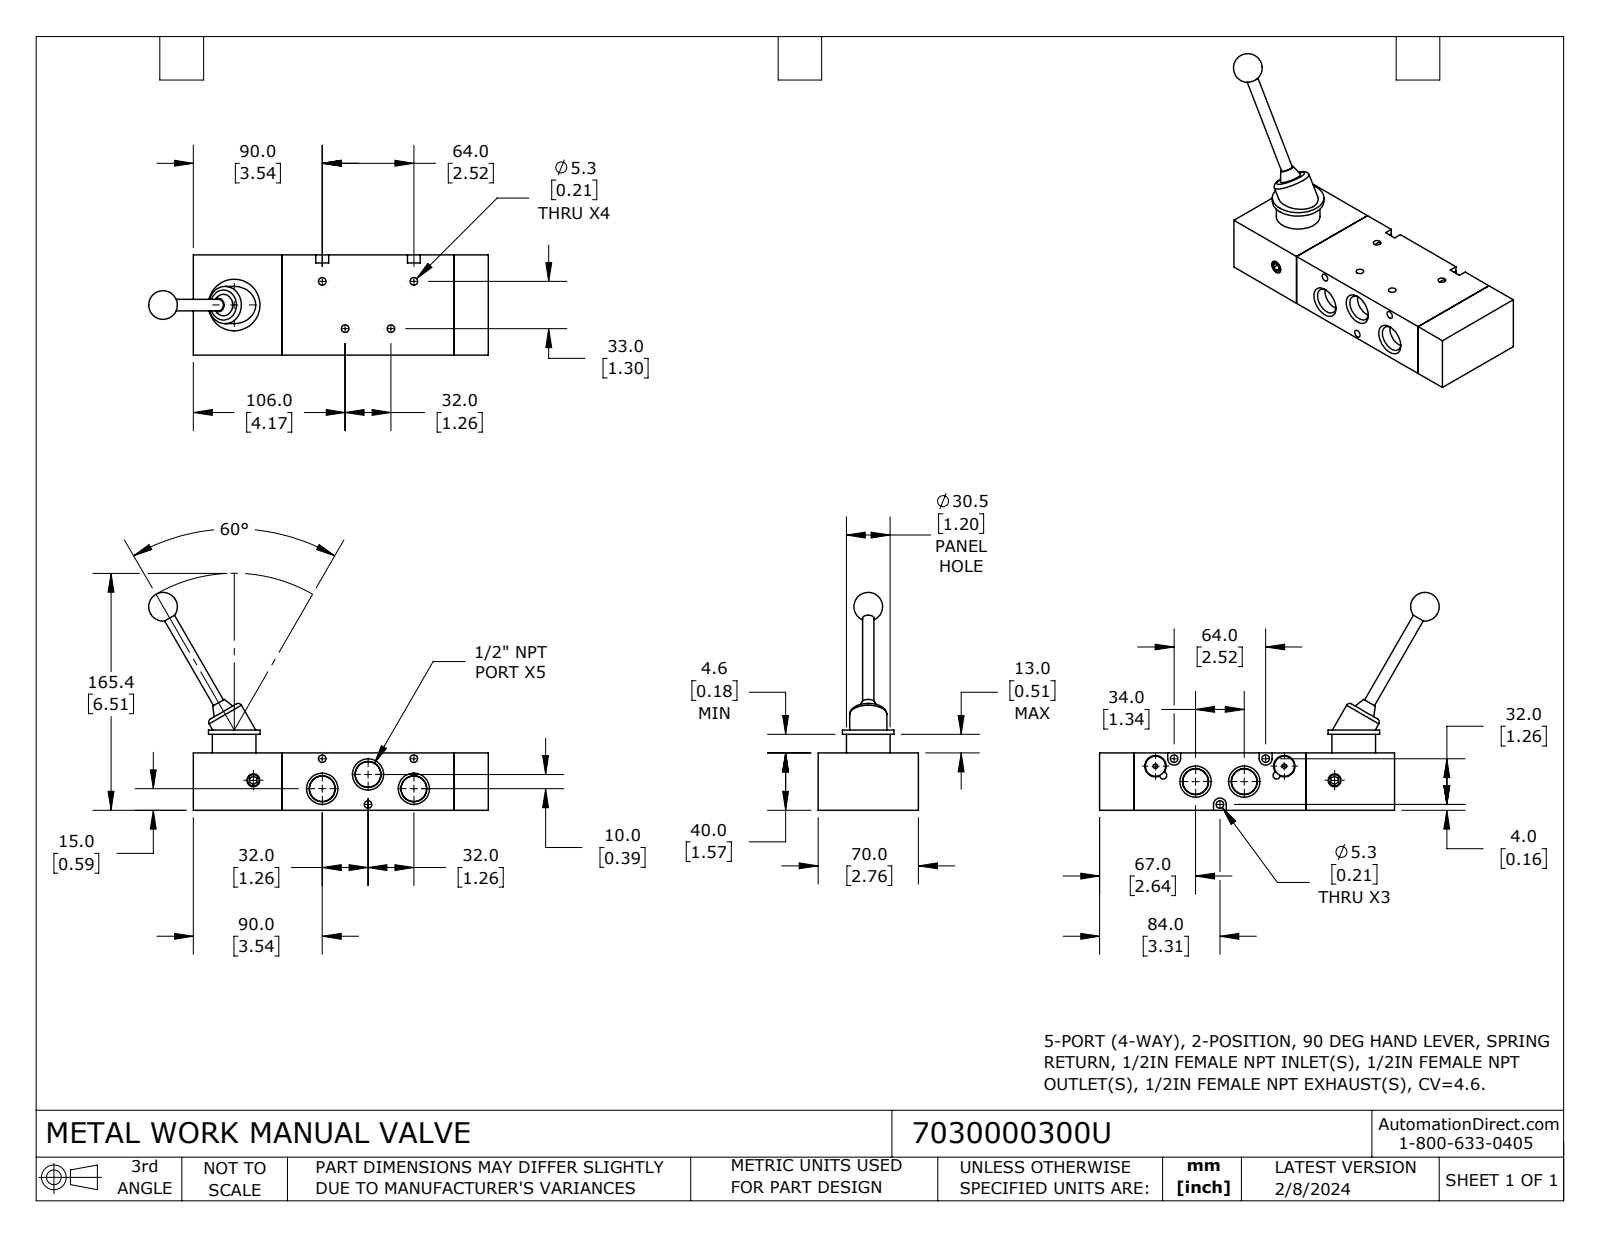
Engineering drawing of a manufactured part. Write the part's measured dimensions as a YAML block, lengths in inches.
part_name: "7030000300U"
step_written_by: "SolidWorks 2023 (CONFIG_CONTROL_DESIGN)"
units: inches
bodies: {solids: 3, faces: 155, planar: 72, cylindrical: 57, other: 26}
overall_size: [9.339, 5.988, 2.756]
volume: 35.65
surface_area: 120.8
round_holes:
  - {diameter: 0.209, count: 7}
  - {diameter: 0.587, count: 2}
  - {diameter: 0.354, count: 1}
round_bosses_or_shafts:
  - {diameter: 0.551, count: 2}
  - {diameter: 1.417, count: 1}
  - {diameter: 1.201, count: 1}
  - {diameter: 1.024, count: 1}
  - {diameter: 0.315, count: 1}
  - {diameter: 0.313, count: 1}
partial_cylinders:
  - {radius: 0.177, count: 3}
  - {radius: 0.098, count: 2}
face_to_face_distances: [1.575, 2.756, 4.724, 0.945, 5.669, 8.11, 7.165, 2.441, 0.354, 2.402]
hole_center_spacings: [0.552, 1.444, 1.781, 2.061, 2.293, 2.52, 3.039, 1.26]
